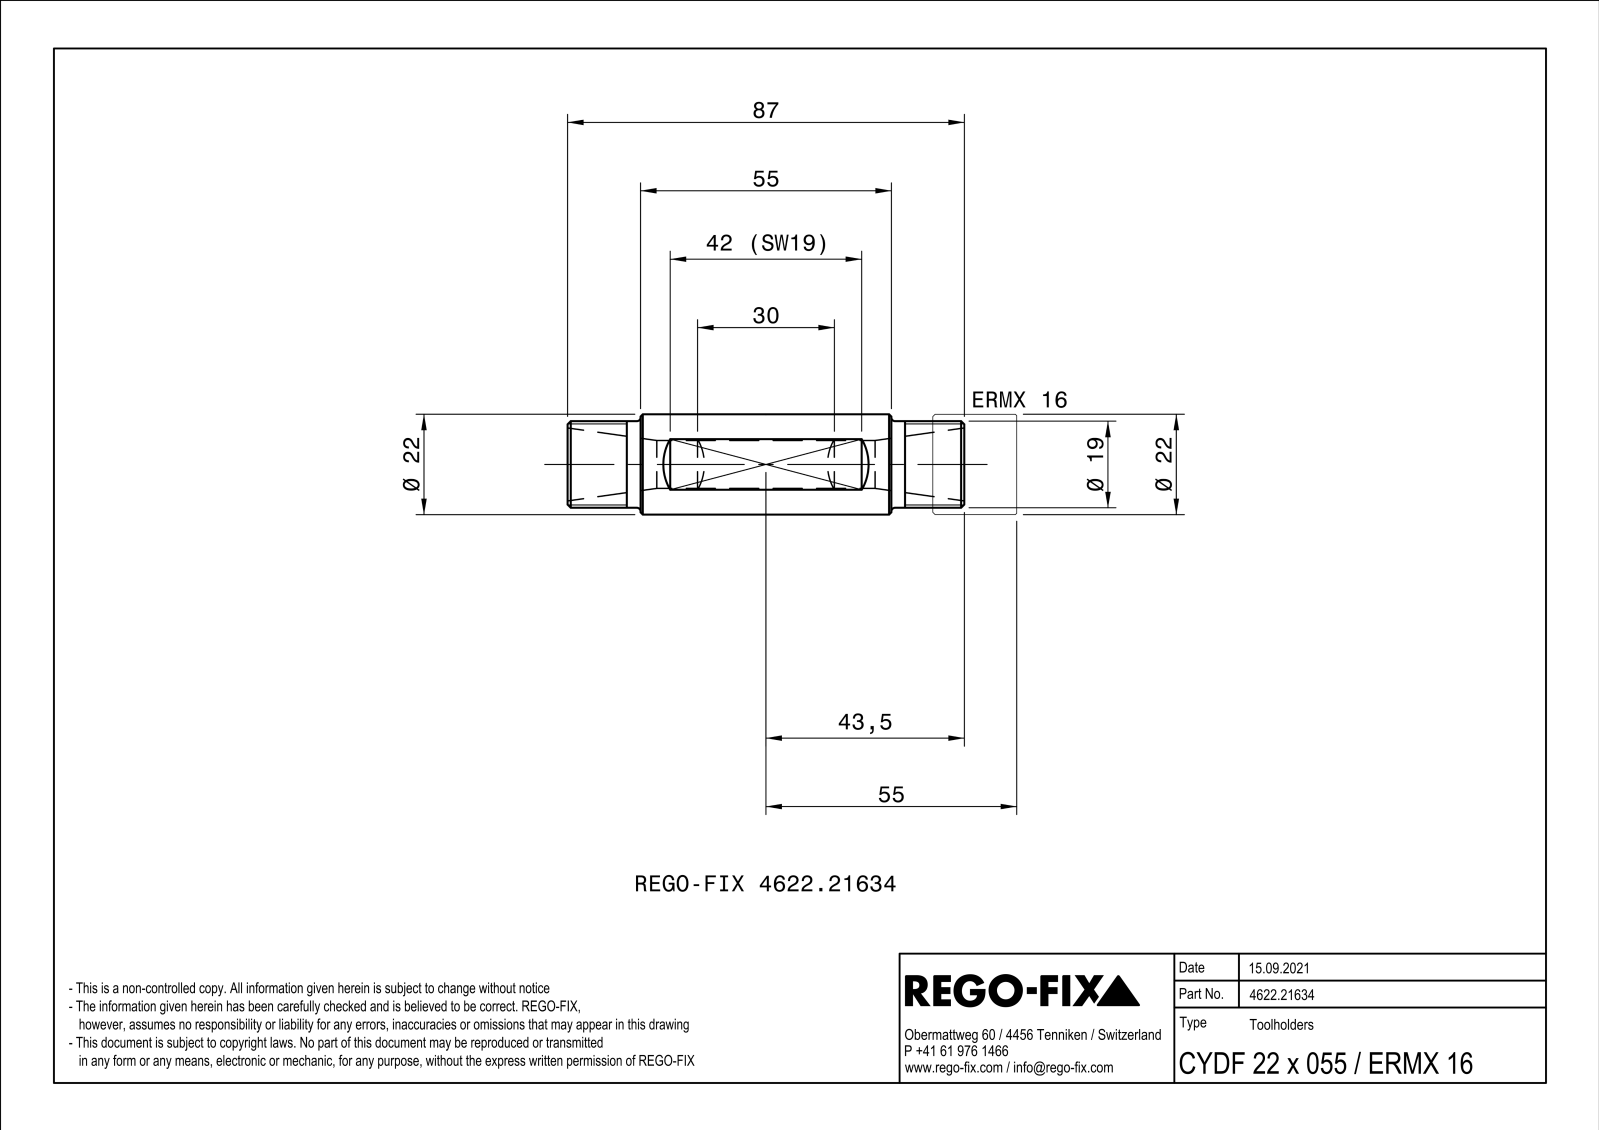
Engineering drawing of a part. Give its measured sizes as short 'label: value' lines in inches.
name: NOCUT
written by: SIEMENS PLM Software Solid Edge ST10 (AUTOMOTIVE_DESIGN)
unit: in
bodies: 1 solid, 29 faces (13 planar, 6 cylindrical, 10 other)
size: 3.425 × 0.866 × 0.866
volume: 1.201 in³; area: 14.18 in²
holes: 1× ⌀0.413
bosses: 1× ⌀0.866, 1× ⌀0.748
face distances: 0.748, 3.425, 0.64, 0.362, 1.002, 0.63, 2.795, 2.165
